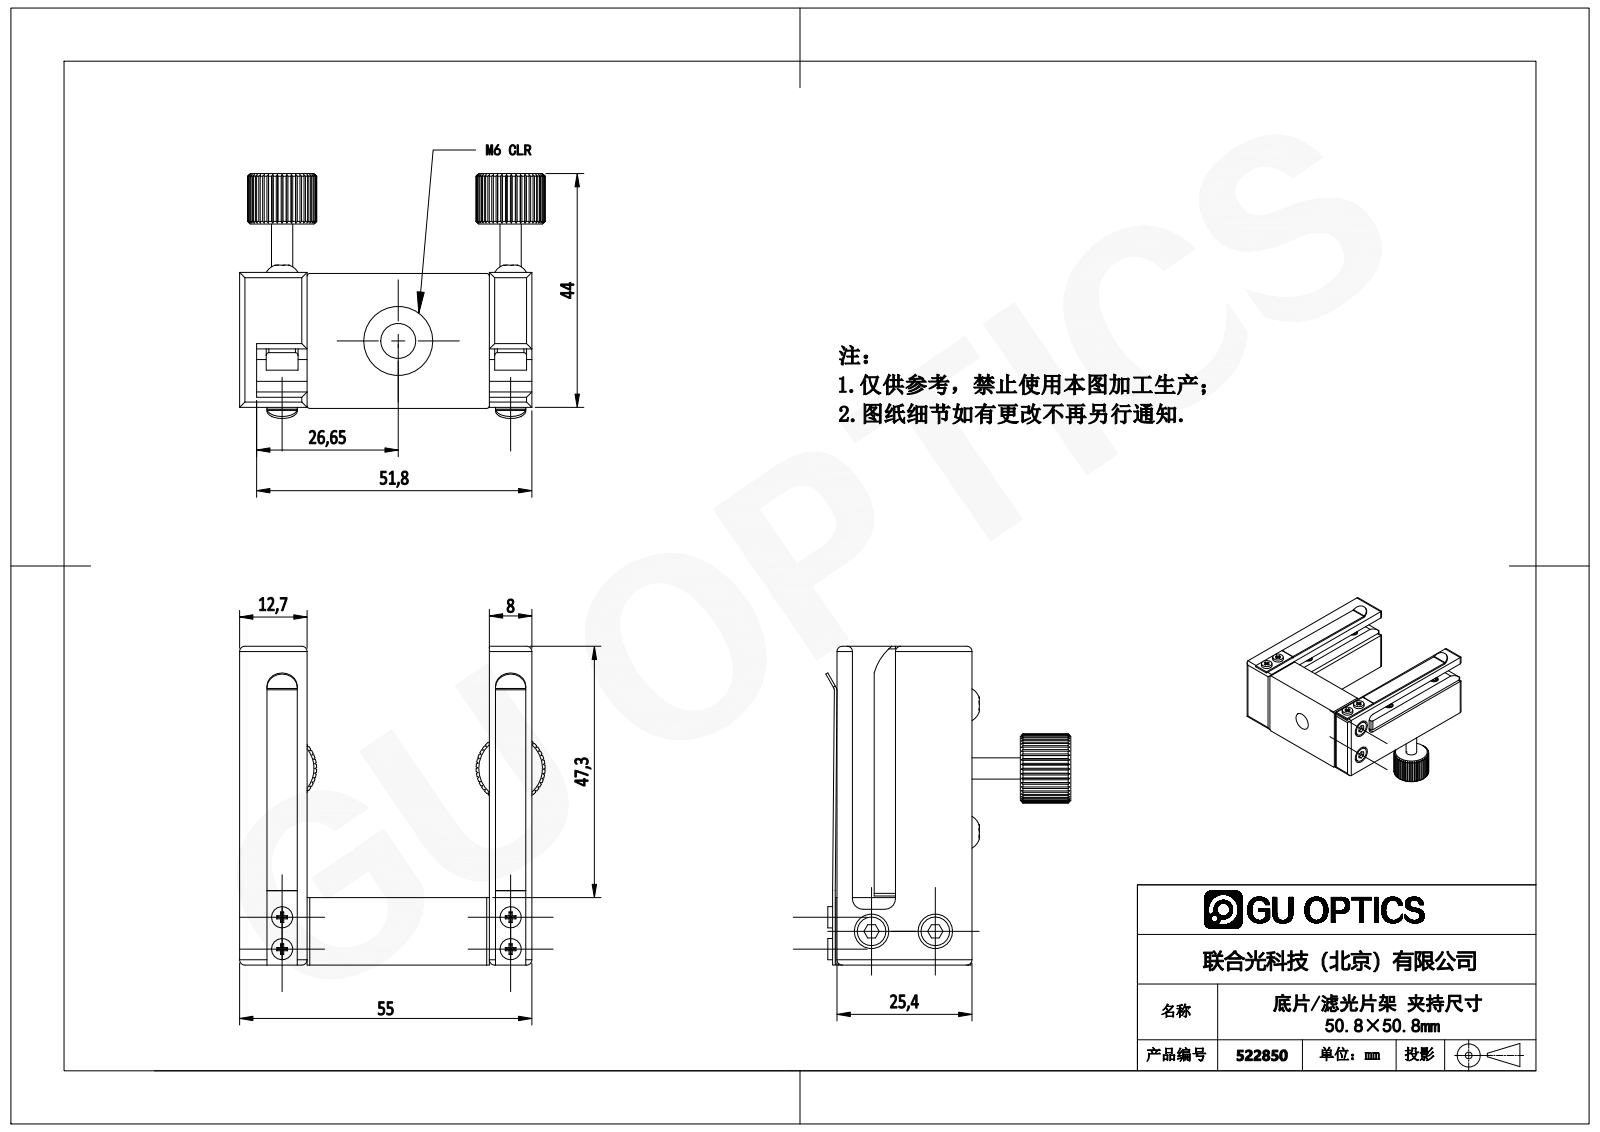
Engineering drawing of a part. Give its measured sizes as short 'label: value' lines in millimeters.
name: PLH-22
written by: SolidWorks 2012 (CONFIG_CONTROL_DESIGN)
unit: mm
bodies: 0 solids, 549 faces (377 planar, 156 cylindrical, 16 other)
size: 60 × 57.5 × 46.1
holes: 4× ⌀3.3, 2× ⌀4.5, 2× ⌀6.5, 2× ⌀7.2, 1× ⌀6.6, 1× ⌀13
bosses: 6× ⌀4, 2× ⌀5.4, 1× ⌀7
rounds: 14× R1, 12× R0.5, 2× R2, 2× R2.85, 2× R6.5, 1× R10
face distances: 12.7, 25.4, 47, 34.3, 11, 14.4, 8, 55, 42.3, 8.1
hole spacings: 12, 44.64, 43, 24, 49.24
